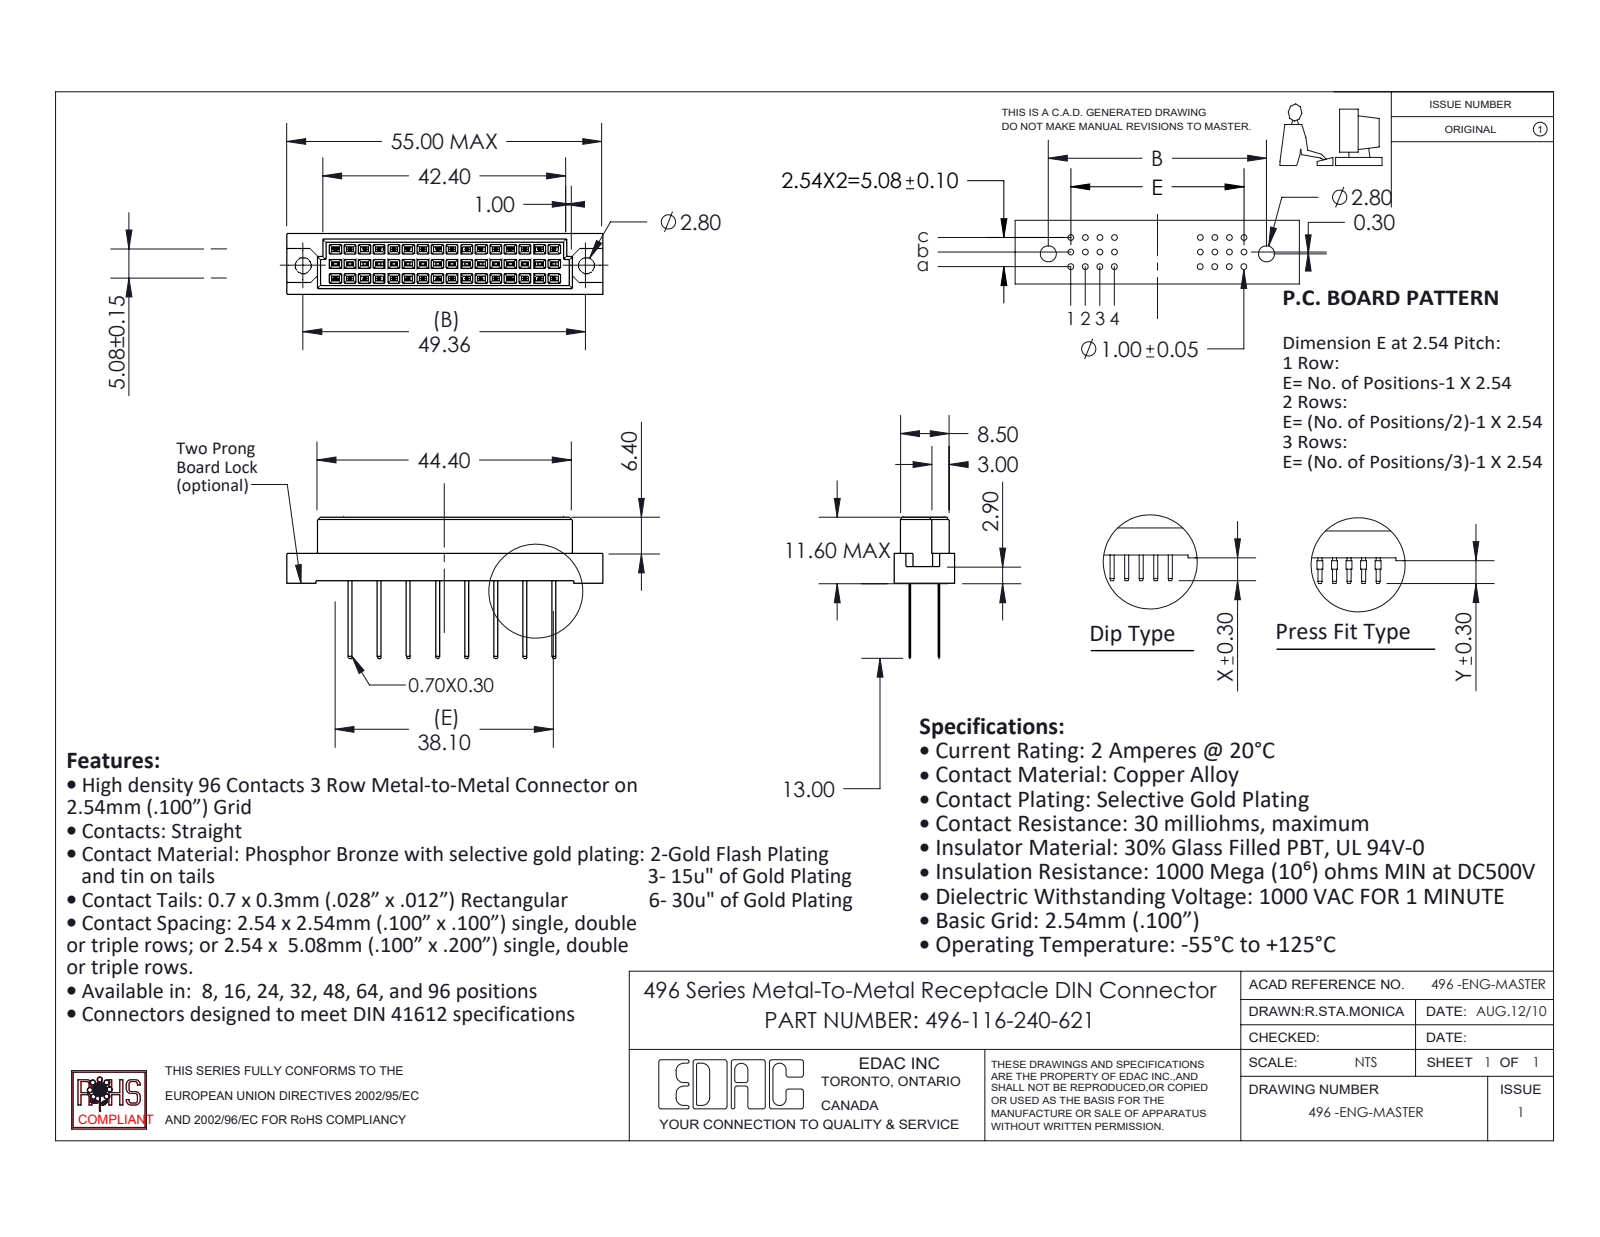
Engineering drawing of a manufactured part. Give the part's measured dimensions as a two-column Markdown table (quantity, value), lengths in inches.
| quantity | value |
| --- | --- |
| part name | 496 Part_48; 496-116-240-621; 496-290_40 |
| STEP written by | SolidWorks 2020 (CONFIG_CONTROL_DESIGN) |
| units | inches |
| bodies | 17 solids, 826 faces (822 planar, 4 cylindrical, 0 other) |
| overall size | 2.165 × 0.969 × 0.417 |
| volume | 0.284 in³ |
| surface area | 7.401 in² |
| round holes (diameter × count) | 0.11 × 2 |
| main face-to-face distances | 0.1, 0.2, 0.041, 0.376, 0.032, 0.022, 0.022, 0.103, 0.115, 0.303 |
| hole center spacings | 1.943 |
